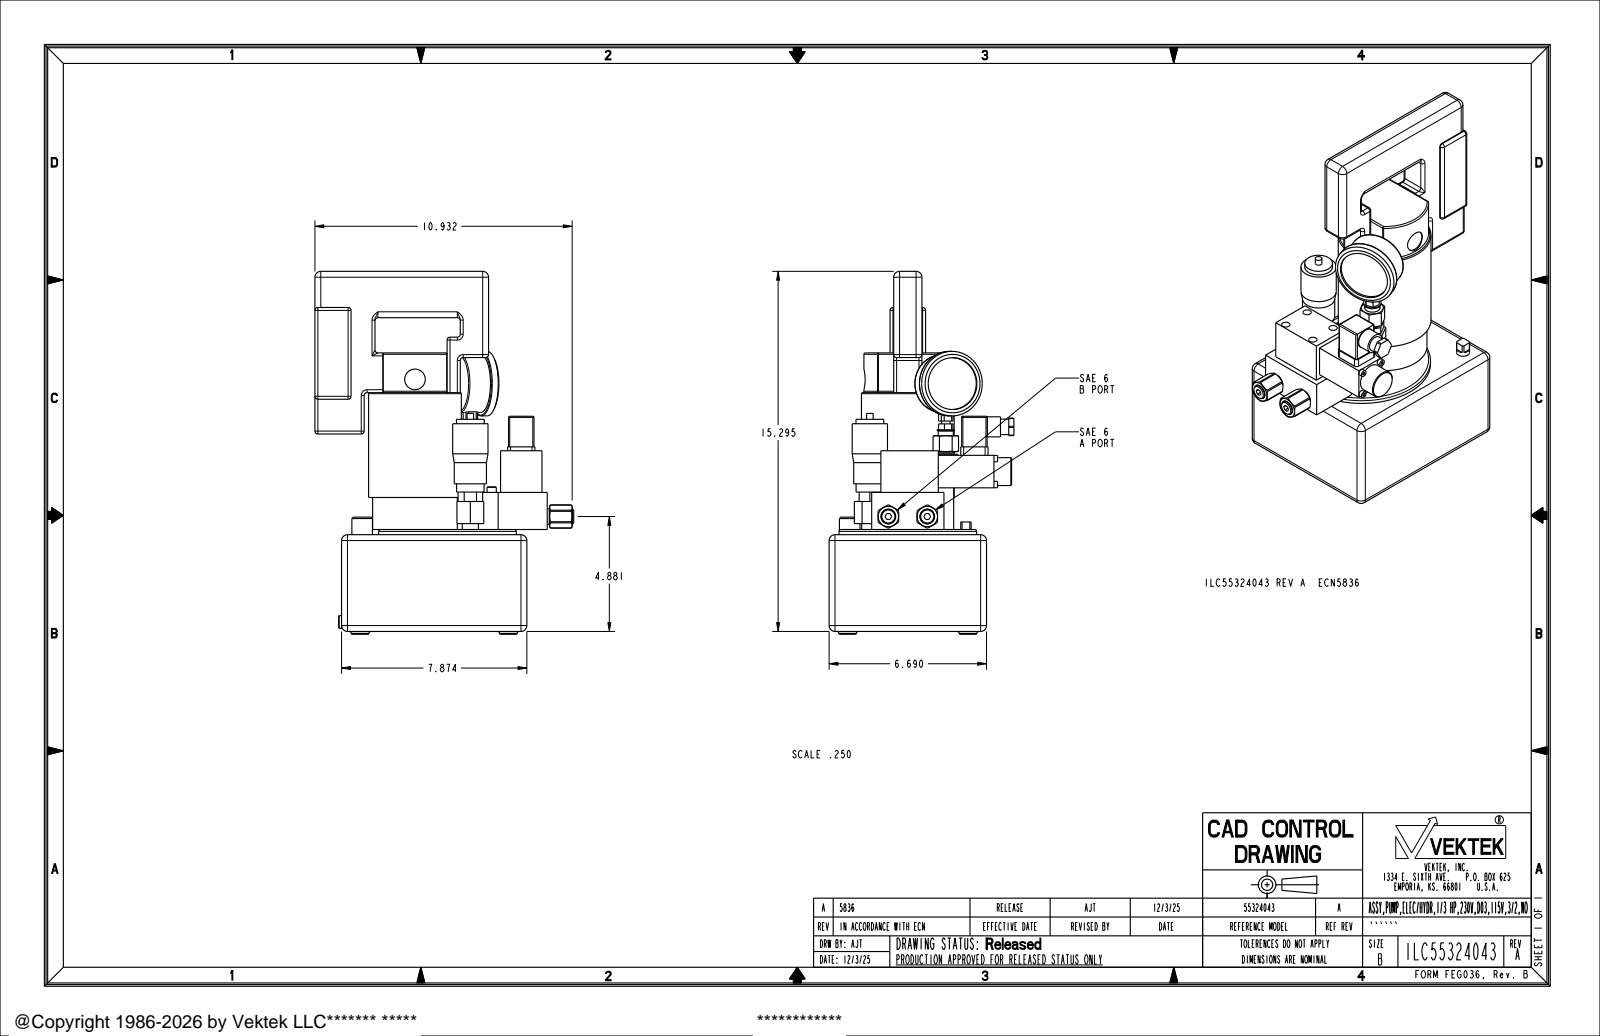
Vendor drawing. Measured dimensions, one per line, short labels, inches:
name: ILC55324043
written by: CREO PARAMETRIC BY PTC INC, 2021164 (CONFIG_CONTROL_DESIGN)
unit: in
bodies: 1 solid, 726 faces (300 planar, 231 cylindrical, 195 other)
size: 15.415 × 10.999 × 7.854
volume: 388.9 in³; area: 556.3 in²
holes: 4× ⌀0.197, 4× ⌀0.354, 1× ⌀0.502, 1× ⌀0.652, 1× ⌀0.71, 1× ⌀0.875, 1× ⌀0.95, 1× ⌀2.2
bosses: 5× ⌀0.75, 4× ⌀0.313, 4× ⌀0.271, 3× ⌀0.394, 1× ⌀5.85, 1× ⌀3.94, 1× ⌀3.6, 1× ⌀2.74
rounds: 48× R0.125, 22× R0.25, 13× R0.05, 8× R0.06, 2× R0.49, 1× R0.314, 1× R1.866
face distances: 2.745, 3.945, 6.69, 7.874, 1.2, 4.11, 4.33, 0.22, 2.589, 4.101
hole spacings: 1.594, 2.026, 5.118, 6.299, 6.507, 8.117, 0.125, 1.22
